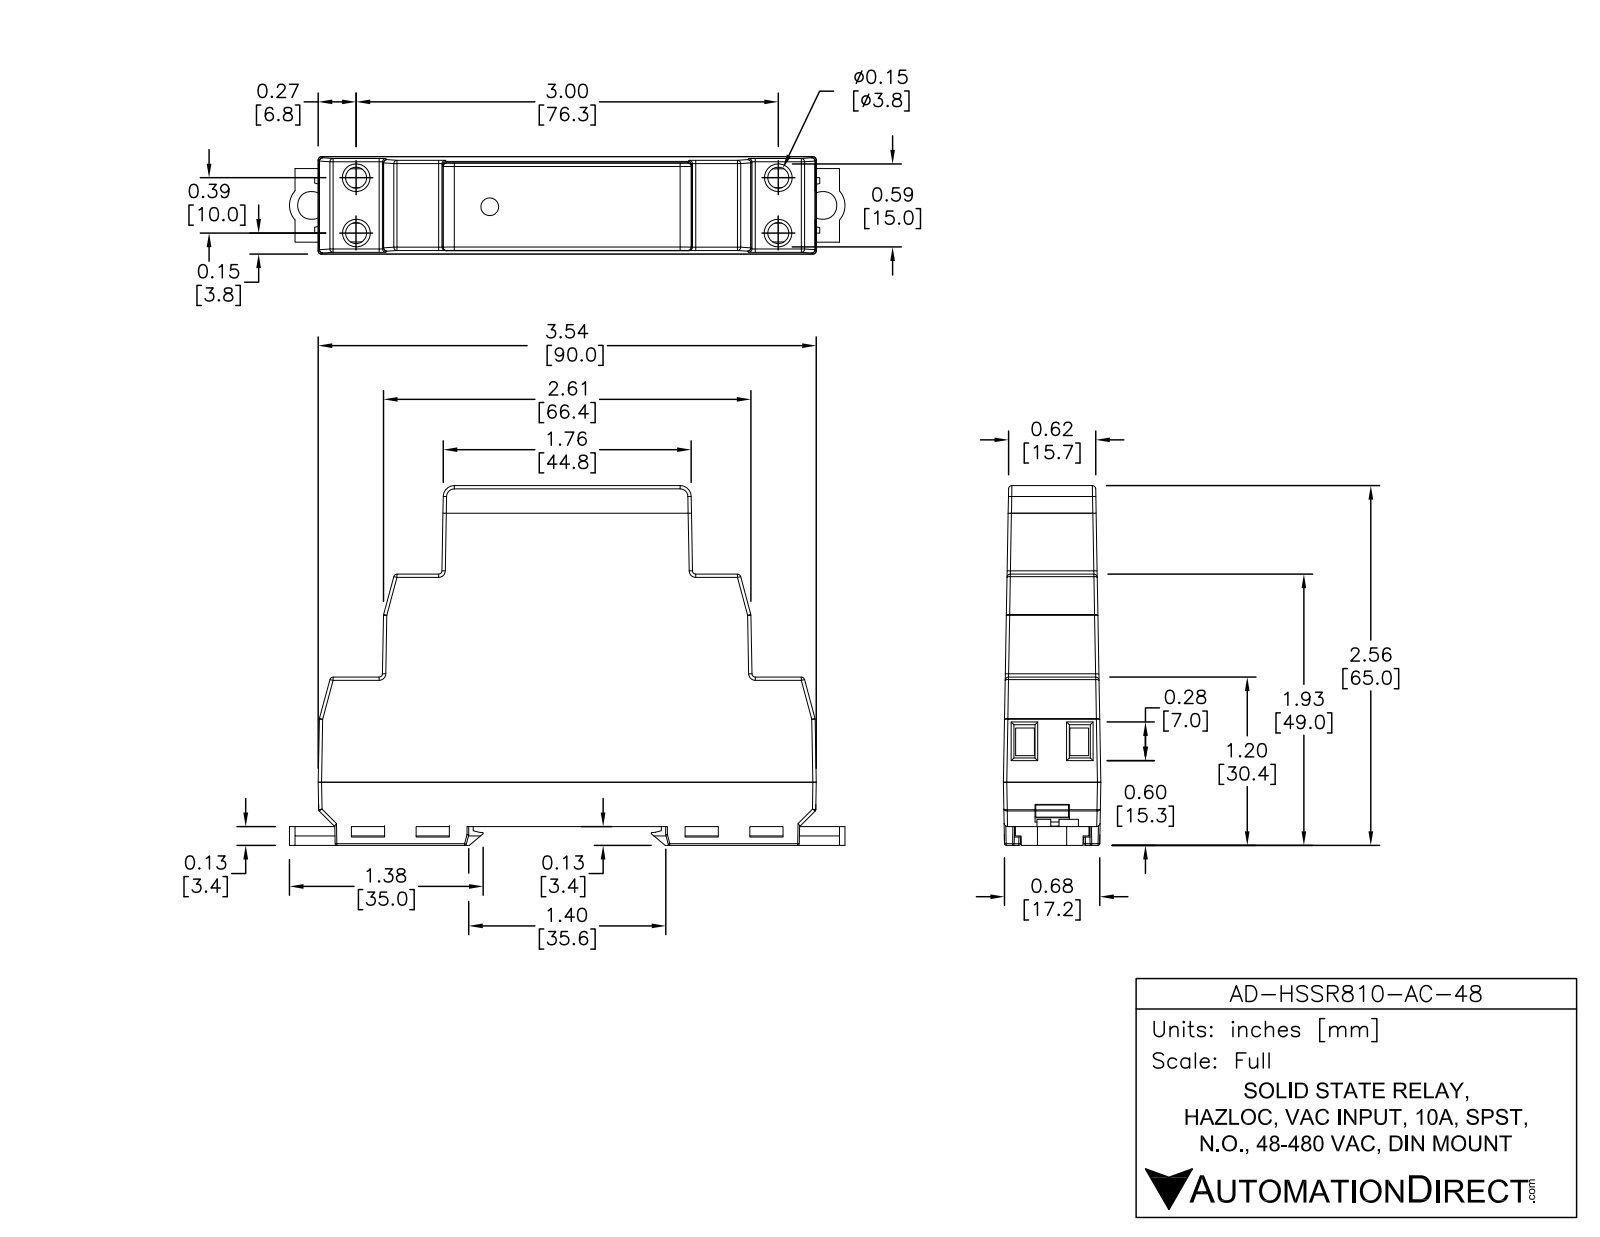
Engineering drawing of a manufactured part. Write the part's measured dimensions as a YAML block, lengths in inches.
part_name: "AD-HSSR810-AC-48"
step_written_by: "SolidWorks 2013 (AUTOMOTIVE_DESIGN)"
units: inches
bodies: {solids: 35, faces: 1271, planar: 710, cylindrical: 65, other: 496}
overall_size: [3.952, 2.619, 0.692]
volume: 4.725
surface_area: 25.55
round_holes:
  - {diameter: 0.2, count: 4}
  - {diameter: 0.19, count: 2}
round_bosses_or_shafts:
  - {diameter: 0.175, count: 4}
  - {diameter: 0.1, count: 1}
partial_cylinders:
  - {radius: 0.02, count: 10}
  - {radius: 0.024, count: 10}
  - {radius: 0.012, count: 6}
  - {radius: 0.079, count: 2}
  - {radius: 0.15, count: 2}
  - {radius: 45.93, count: 2}
face_to_face_distances: [0.136, 2.559, 2.423, 0.134, 2.425, 1.929, 1.795, 1.793, 0.63, 1.197]
hole_center_spacings: [3.335, 0.379, 0.38, 0.4, 3.006, 3.033, 3.652]
